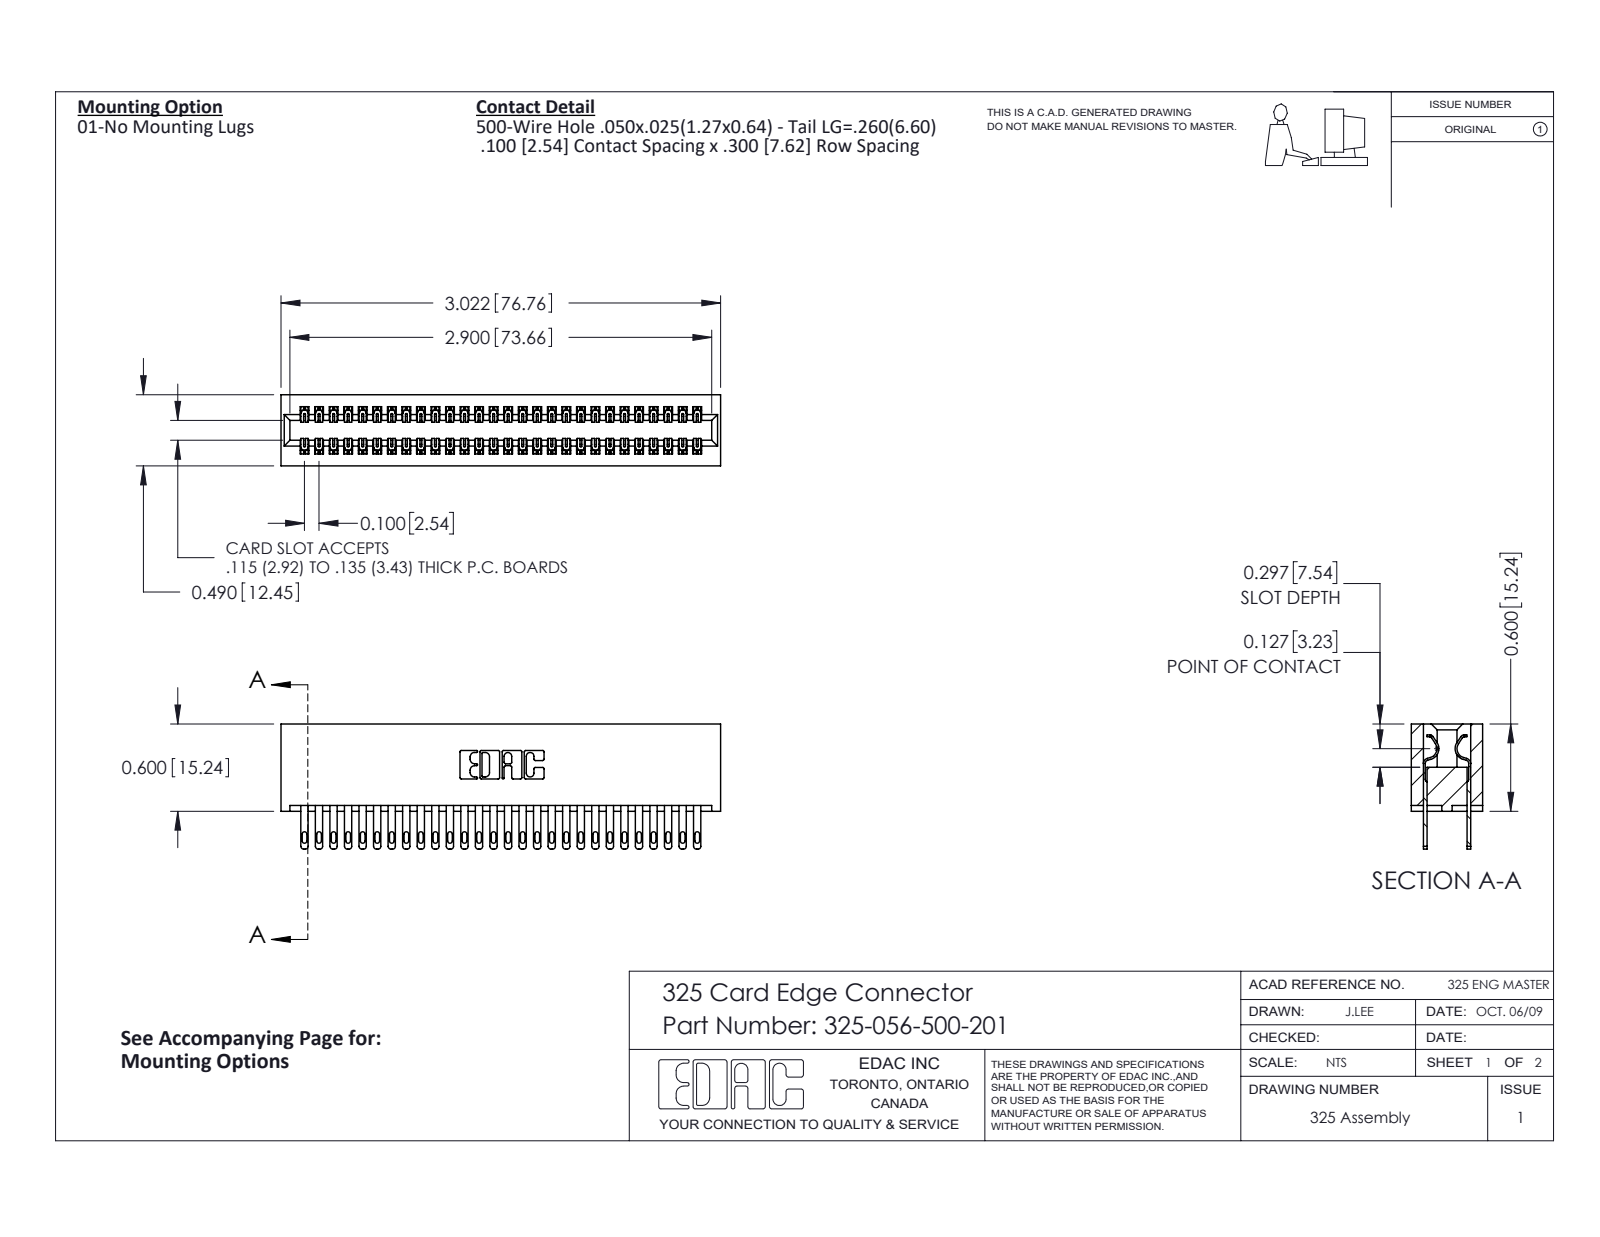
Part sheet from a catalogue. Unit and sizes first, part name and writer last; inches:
Units: inches
Overall size (bounding box): 3.022 × 0.86 × 0.49
Partial cylindrical surfaces — rounded edges, fillets, slot ends (radius × count): R0.006 ×84, R0.016 ×56, R0.02 ×56, R0.01 ×22, R0.007 ×6, R0.031 ×6, R0.026 ×3, R0.014 ×2
Main face-to-face distances: 0.083, 0.407, 0.3, 0.107, 0.383, 0.025, 0.325, 0.49, 0.275, 0.56
Volume: 0.644 in³ · Surface area: 21.23 in²
Bodies: 57 solids, 2794 faces (1746 planar, 1048 cylindrical, 0 other)
Part name (STEP PRODUCT): 325 Part_Lugless; 325-056-500-201; 325-292-001_325-293-100
STEP written by: SolidWorks 2016 (CONFIG_CONTROL_DESIGN)
